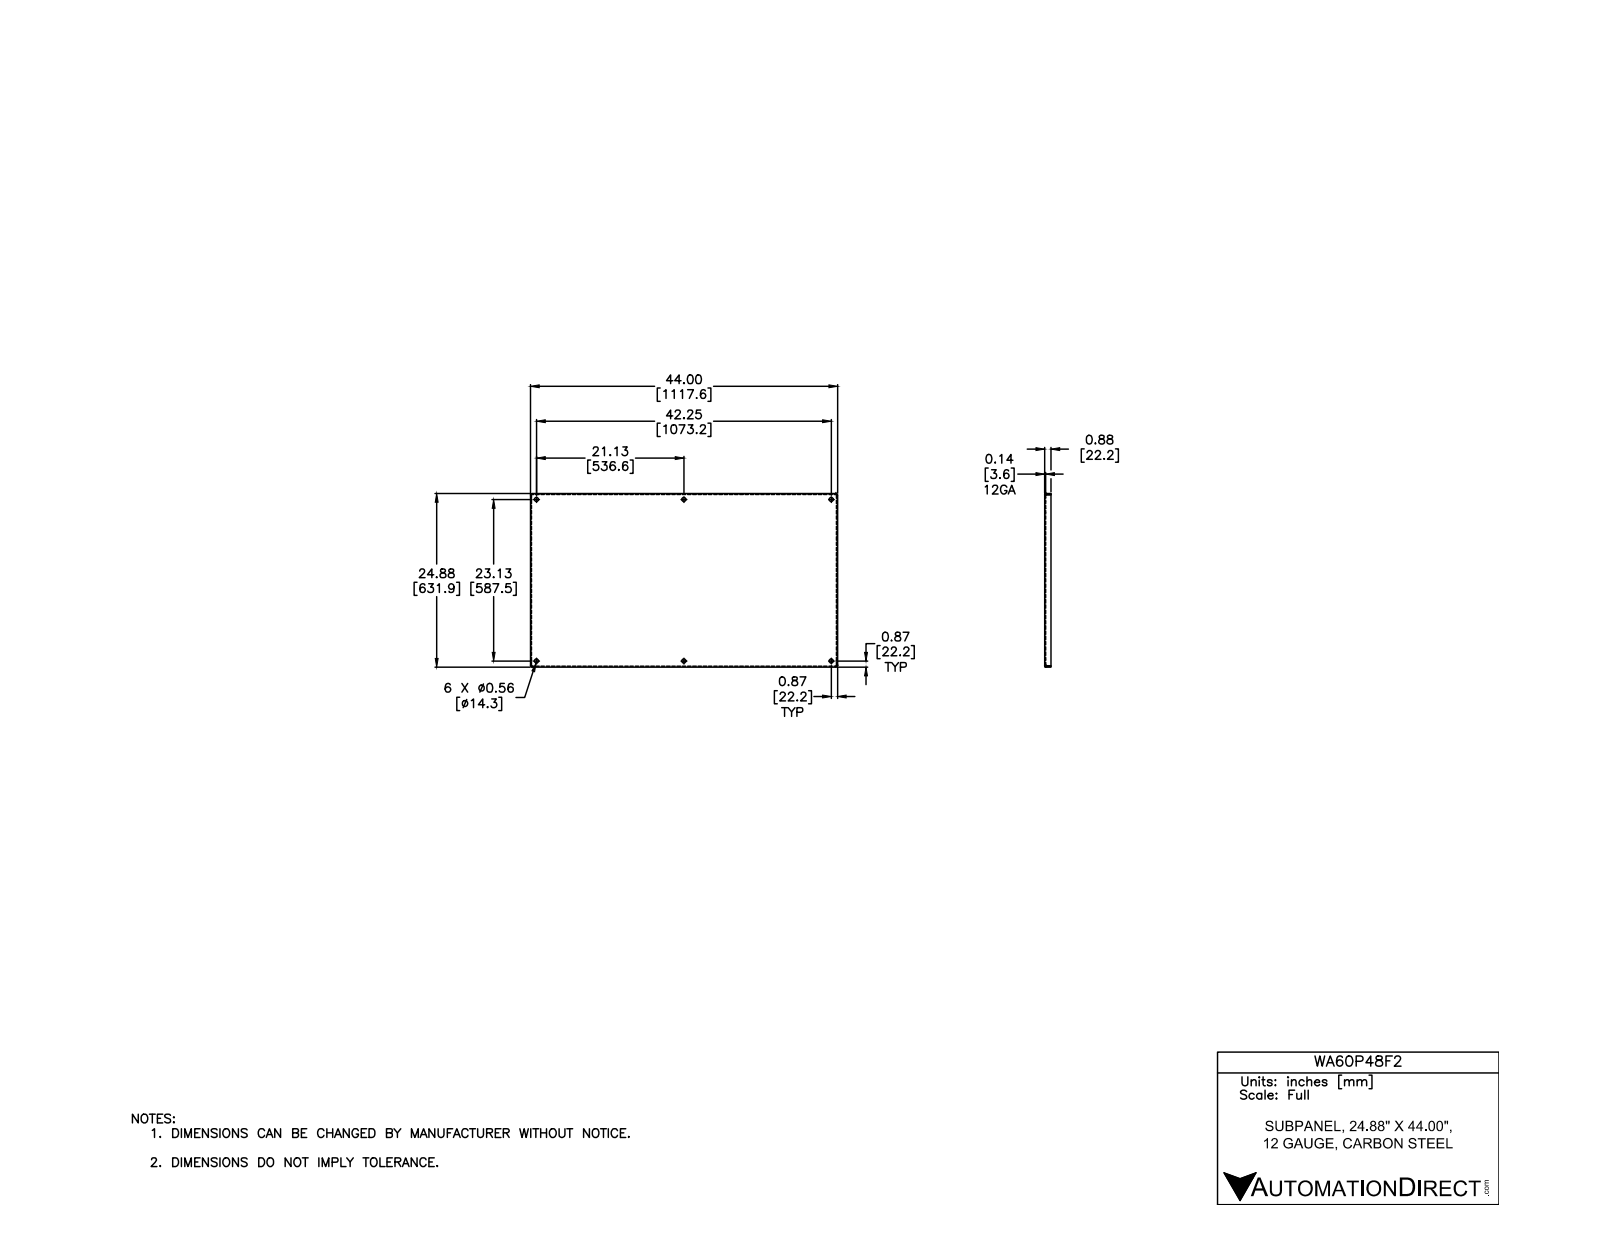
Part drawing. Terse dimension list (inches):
name: WA_P_F
written by: Autodesk Inventor 2012 (AUTOMOTIVE_DESIGN)
unit: in
bodies: 1 solid, 44 faces (22 planar, 14 cylindrical, 8 other)
size: 44 × 24.88 × 0.875
volume: 148.7 in³; area: 2 399 in²
holes: 6× ⌀0.563
rounds: 4× R0.031, 4× R0.156
face distances: 0.125, 0.125, 43.875, 24.88, 24.755, 24.755, 24.63, 44, 43.75, 0.75
hole spacings: 21.125, 23.13, 31.325, 31.326, 42.25, 48.167, 23.13
